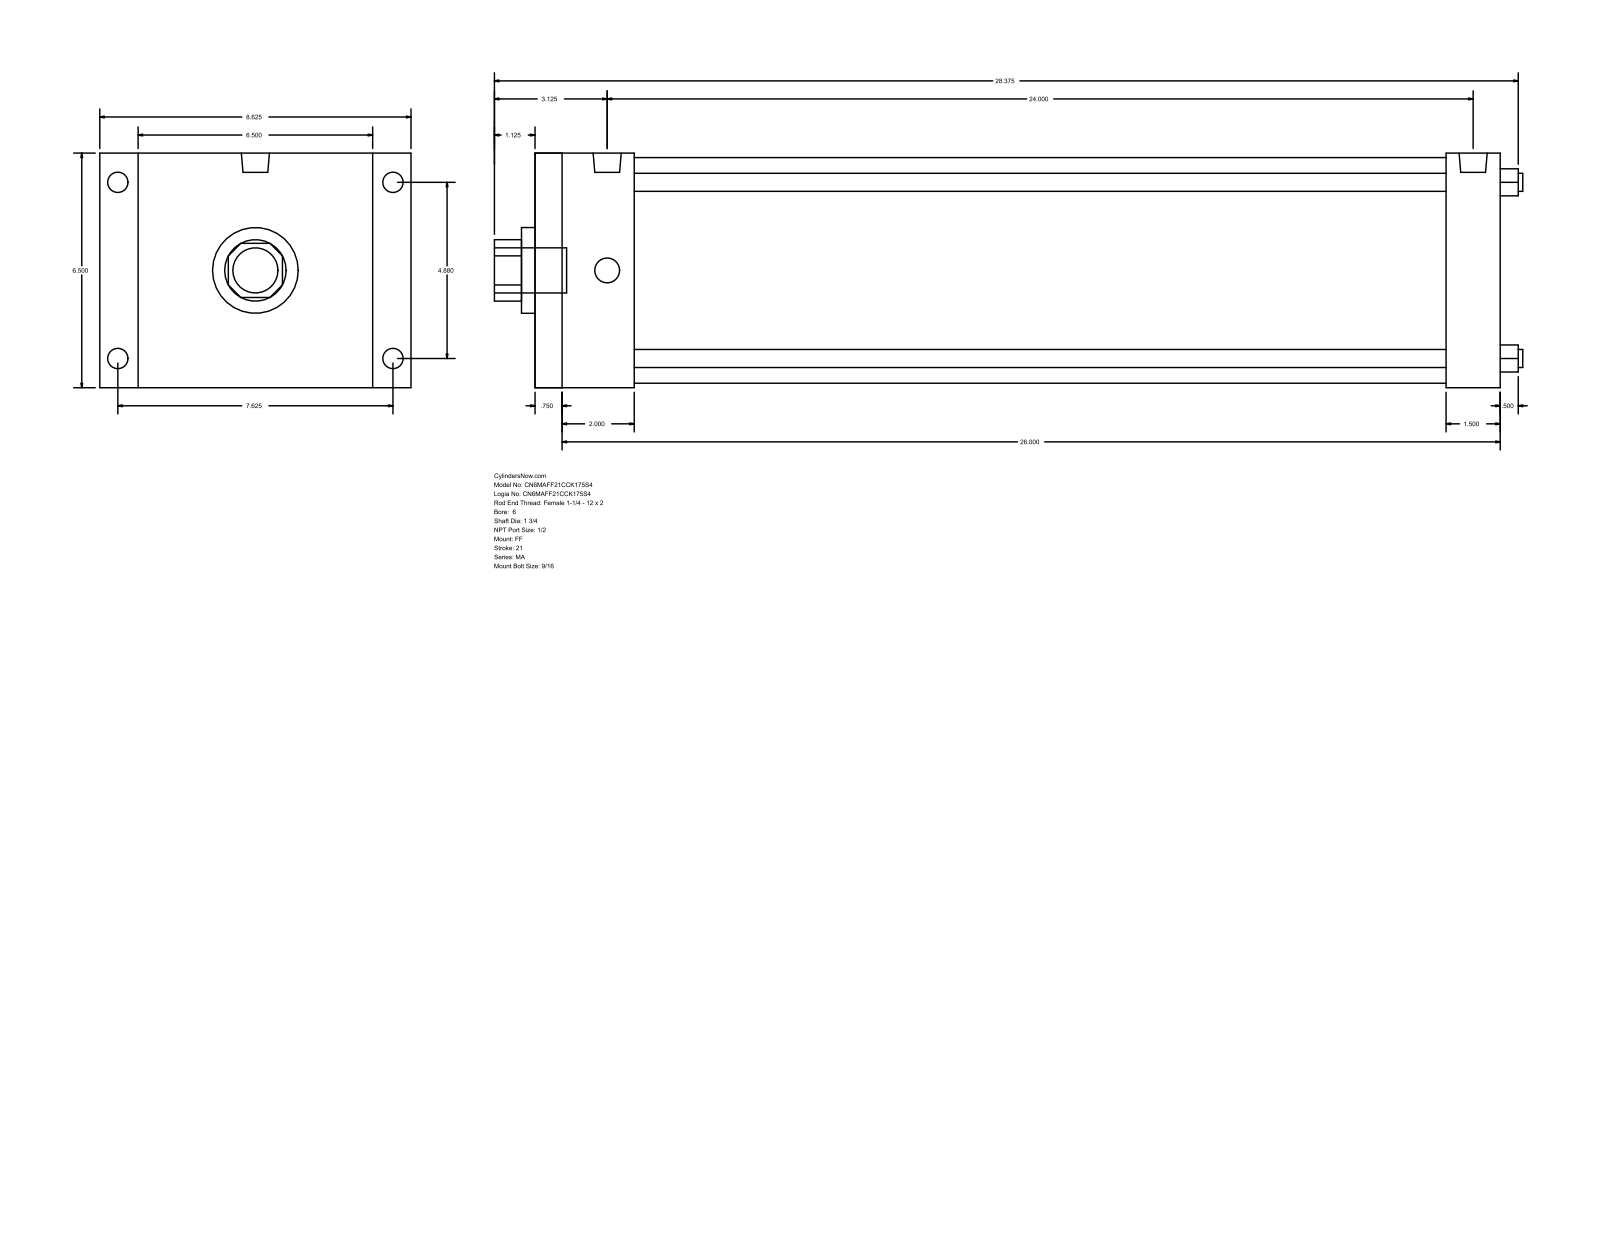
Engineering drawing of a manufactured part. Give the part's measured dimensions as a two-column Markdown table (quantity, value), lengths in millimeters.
| quantity | value |
| --- | --- |
| part name | MA_FF__0600_1.75 |
| STEP written by | GSSL Pune (CONFIG_CONTROL_DESIGN) |
| units | millimeters |
| bodies | 0 solids, 92 faces (64 planar, 28 cylindrical, 0 other) |
| overall size | 723.9 × 219.07 × 165.1 |
| round holes (diameter × count) | 12.7 × 4, 44.45 × 1, 60.33 × 1, 158.75 × 1 |
| round bosses / shafts (diameter × count) | 17.46 × 4, 14.29 × 4, 19.77 × 2, 31.75 × 1 |
| partial cylindrical surfaces (radius × count) | 21.63 × 1 |
| main face-to-face distances | 165.1, 679.45, 19.05, 660.4, 38.1, 50.8, 69.85, 609.6, 641.35, 622.3 |
| hole center spacings | 87.65, 123.96, 175.31 |
